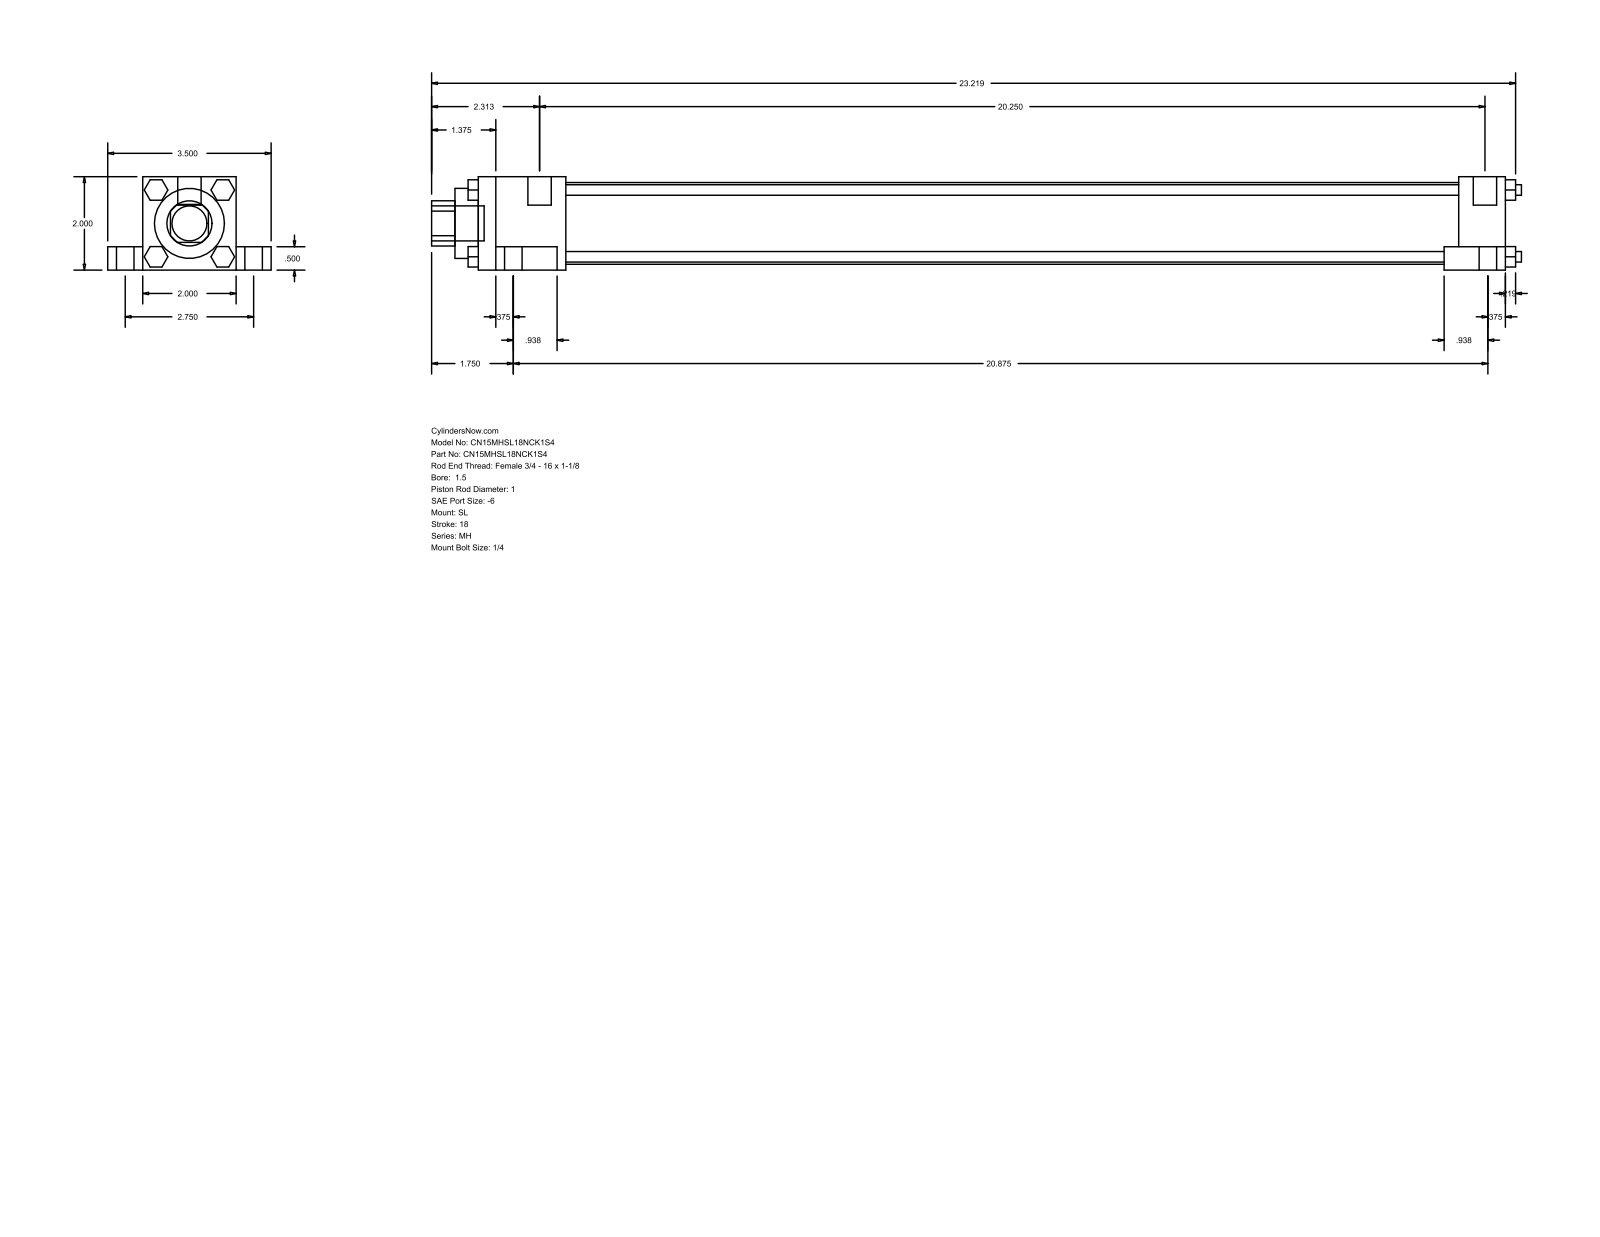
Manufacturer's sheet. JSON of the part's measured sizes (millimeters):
{"part_name": "MH_SL__0150_1", "step_written_by": "GSSL Pune (CONFIG_CONTROL_DESIGN)", "units": "millimeters", "bodies": {"solids": 0, "faces": 148, "planar": 112, "cylindrical": 36, "other": 0}, "overall_size": [592.93, 88.9, 50.8], "round_holes": [[25.4, 1], [38.1, 1], [44.45, 1]], "round_bosses_or_shafts": [[15.88, 4], [9.53, 4], [5.71, 4], [5.56, 4], [12.7, 2], [19.05, 1]], "partial_cylinders_radius": [[12.29, 1]], "face_to_face_distances": [50.8, 12.7, 38.1, 19.05, 69.85, 558.8, 25.4, 9.52, 33.34, 515.94]}
